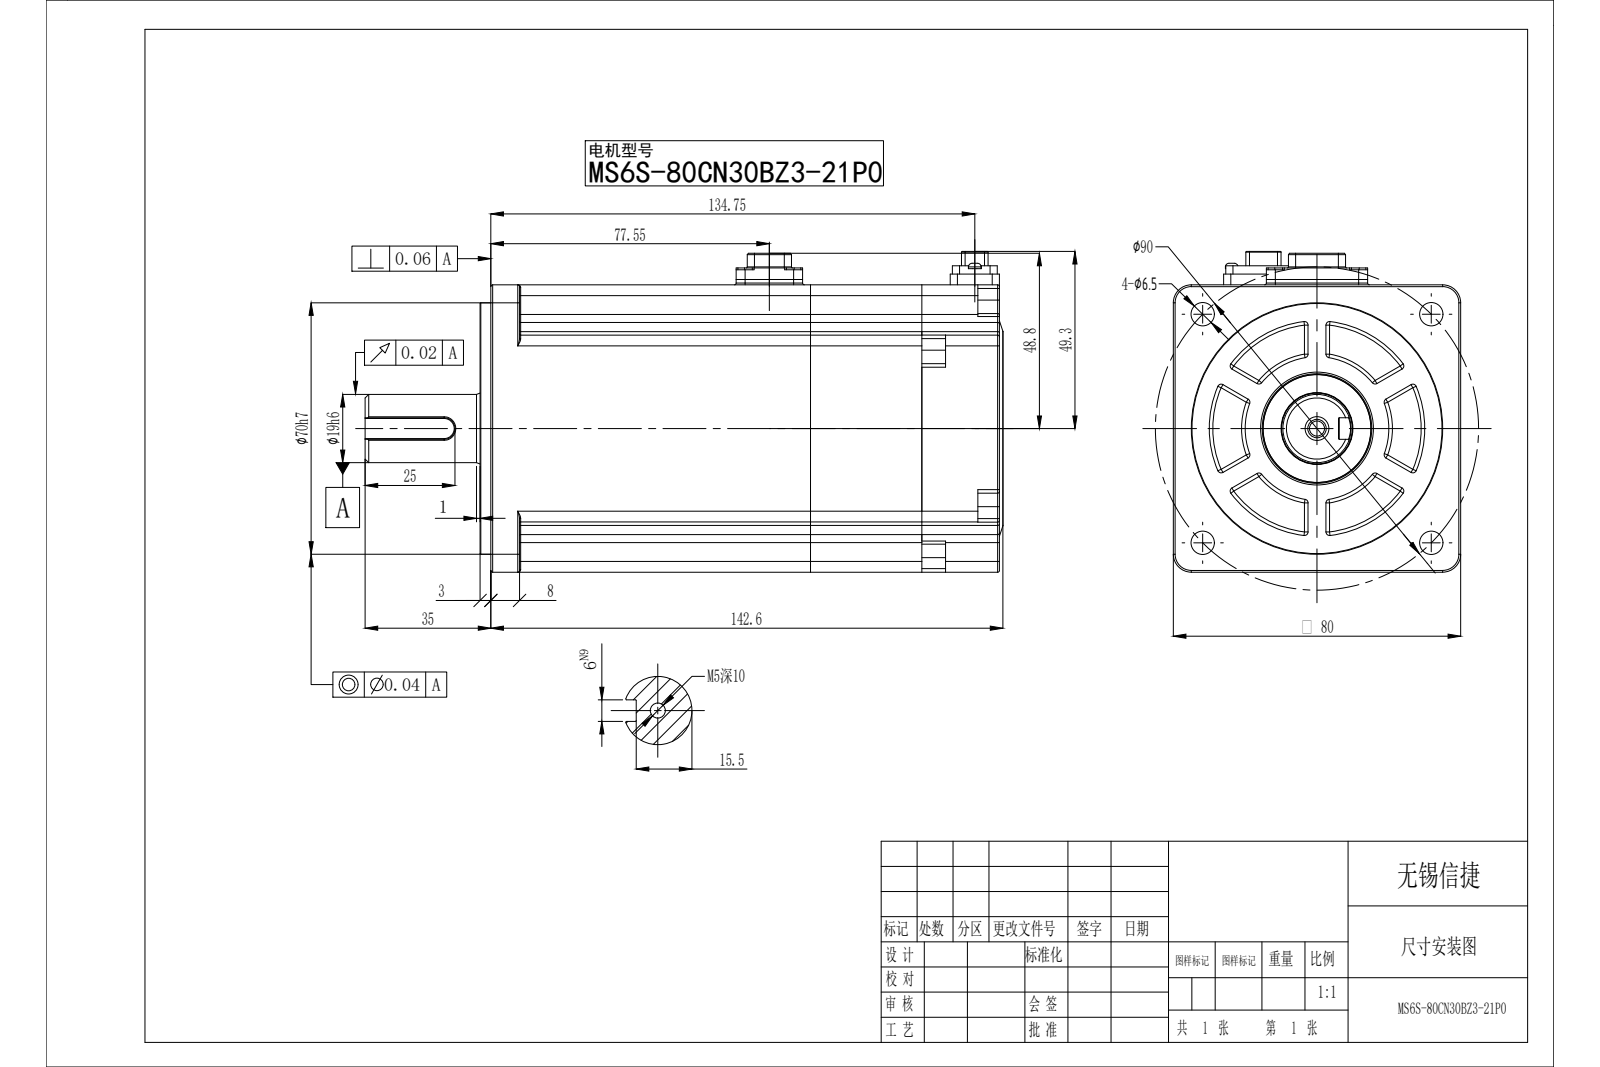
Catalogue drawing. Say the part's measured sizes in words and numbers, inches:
Its 3-D file was written by "SolidWorks 2016 (CONFIG_CONTROL_DESIGN)". It is 0 solids with 864 faces: 366 planar, 314 cylindrical and 184 other. Overall it measures 7.007 by 3.528 by 3.159 inches. Round holes: 4 of diameter 0.083, 4 of diameter 0.256, 2 of diameter 0.063, 1 of diameter 0.165, 1 of diameter 0.787. Round bosses or shafts: 8 of diameter 0.276, 4 of diameter 0.22, 4 of diameter 0.157, 2 of diameter 0.138, 1 of diameter 2.756, 1 of diameter 1.181, 1 of diameter 0.78, 1 of diameter 0.748. Partial cylindrical surfaces (rounded edges, fillets, slot ends): 50 of radius 0.039, 37 of radius 0.02, 37 of radius 0.118, 18 of radius 0.012, 14 of radius 0.008, 12 of radius 0.079, 8 of radius 0.148, 5 of radius 0.098. The main face-to-face distances are 3.15, 3.15, 3.151, 0.551, 2.598, 2.599, 0.552, 2.047, 5.575, 3.149. The hole center spacings are 1.771, 2.506, 0.315, 0.654, 0.726, 1.772, 3.543, 0.925.
